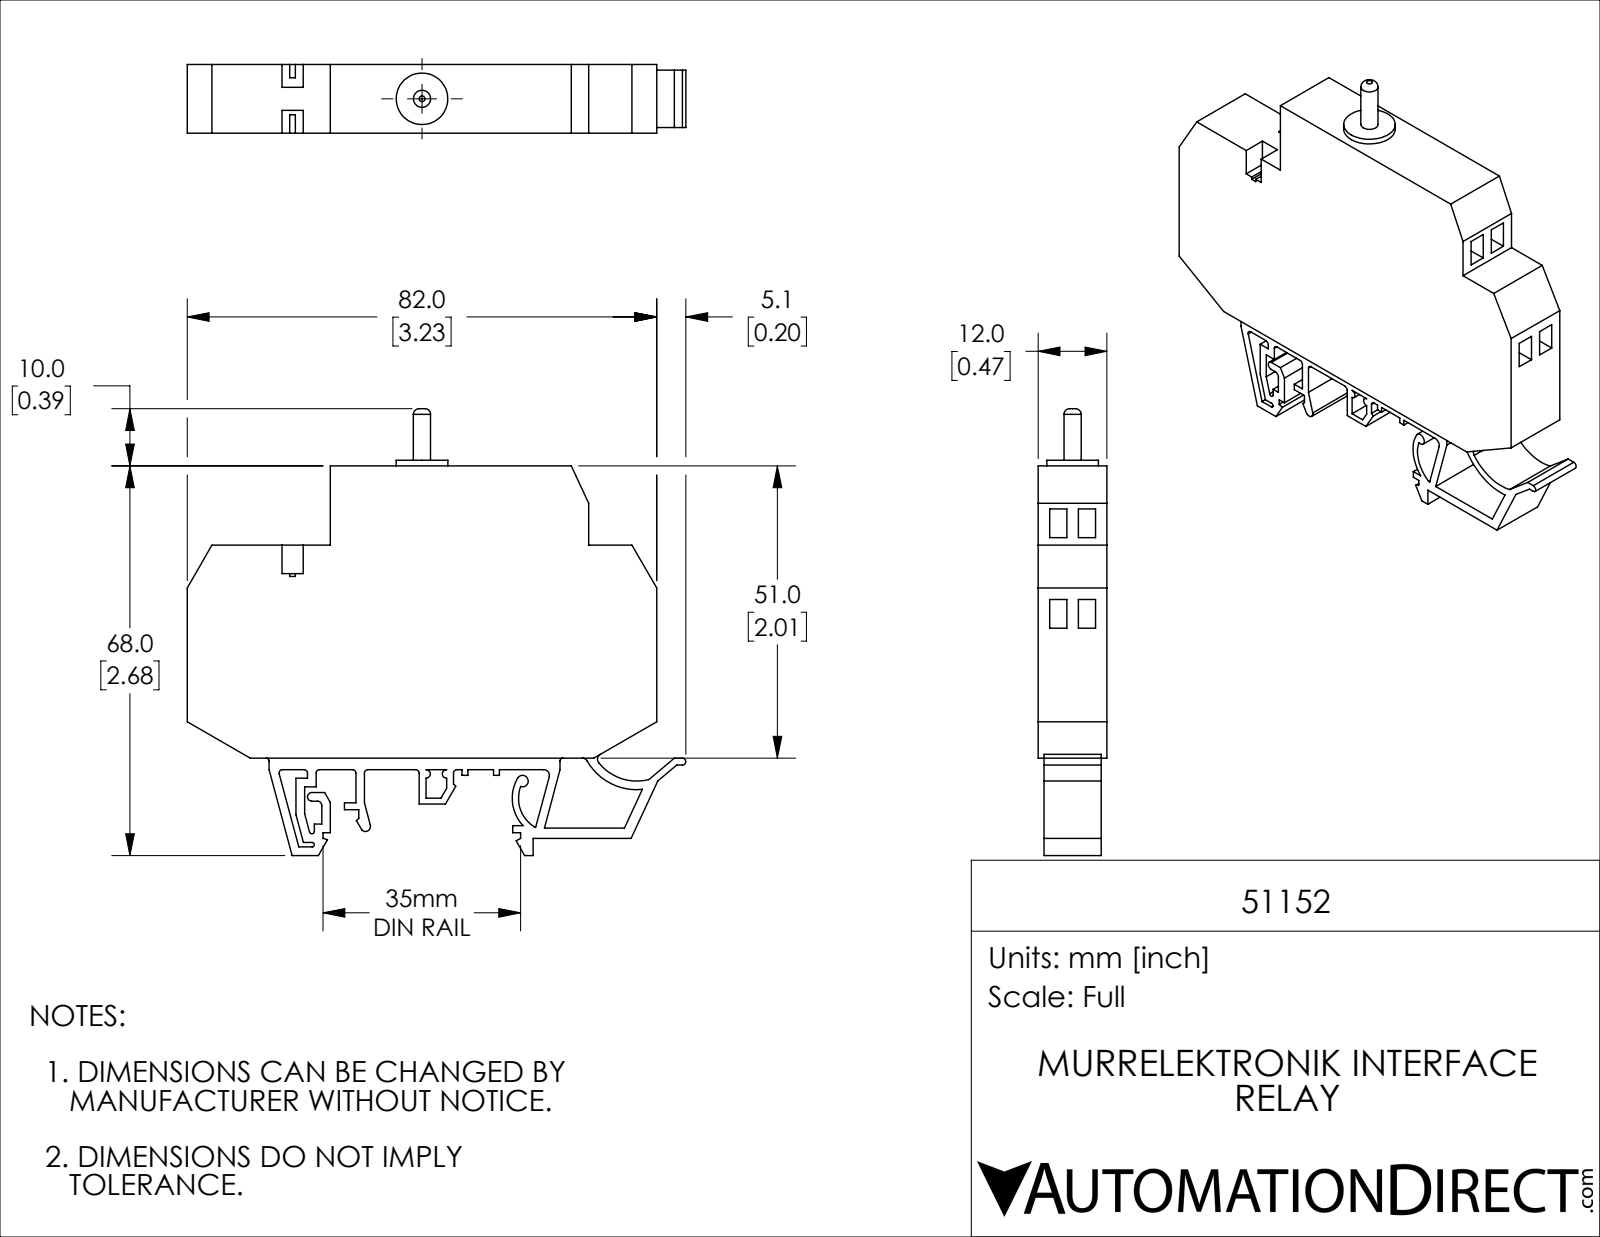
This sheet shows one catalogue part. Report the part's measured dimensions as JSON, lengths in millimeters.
{"part_name": "51152", "step_written_by": "SolidWorks 2019 (CONFIG_CONTROL_DESIGN)", "units": "millimeters", "bodies": {"solids": 1, "faces": 184, "planar": 147, "cylindrical": 35, "other": 2}, "overall_size": [87.1, 78, 12], "volume_mm3": 45540, "surface_area_mm2": 14350, "round_bosses_or_shafts": [[9, 1], [3, 1]], "partial_cylinders_radius": [[0.6, 8], [0.8, 4], [1, 4], [0.5, 2], [0.4, 1], [0.4, 1], [0.9, 1], [5.9, 1]], "face_to_face_distances": [12, 1, 11, 5, 2, 10, 1.5, 6, 53, 3]}
